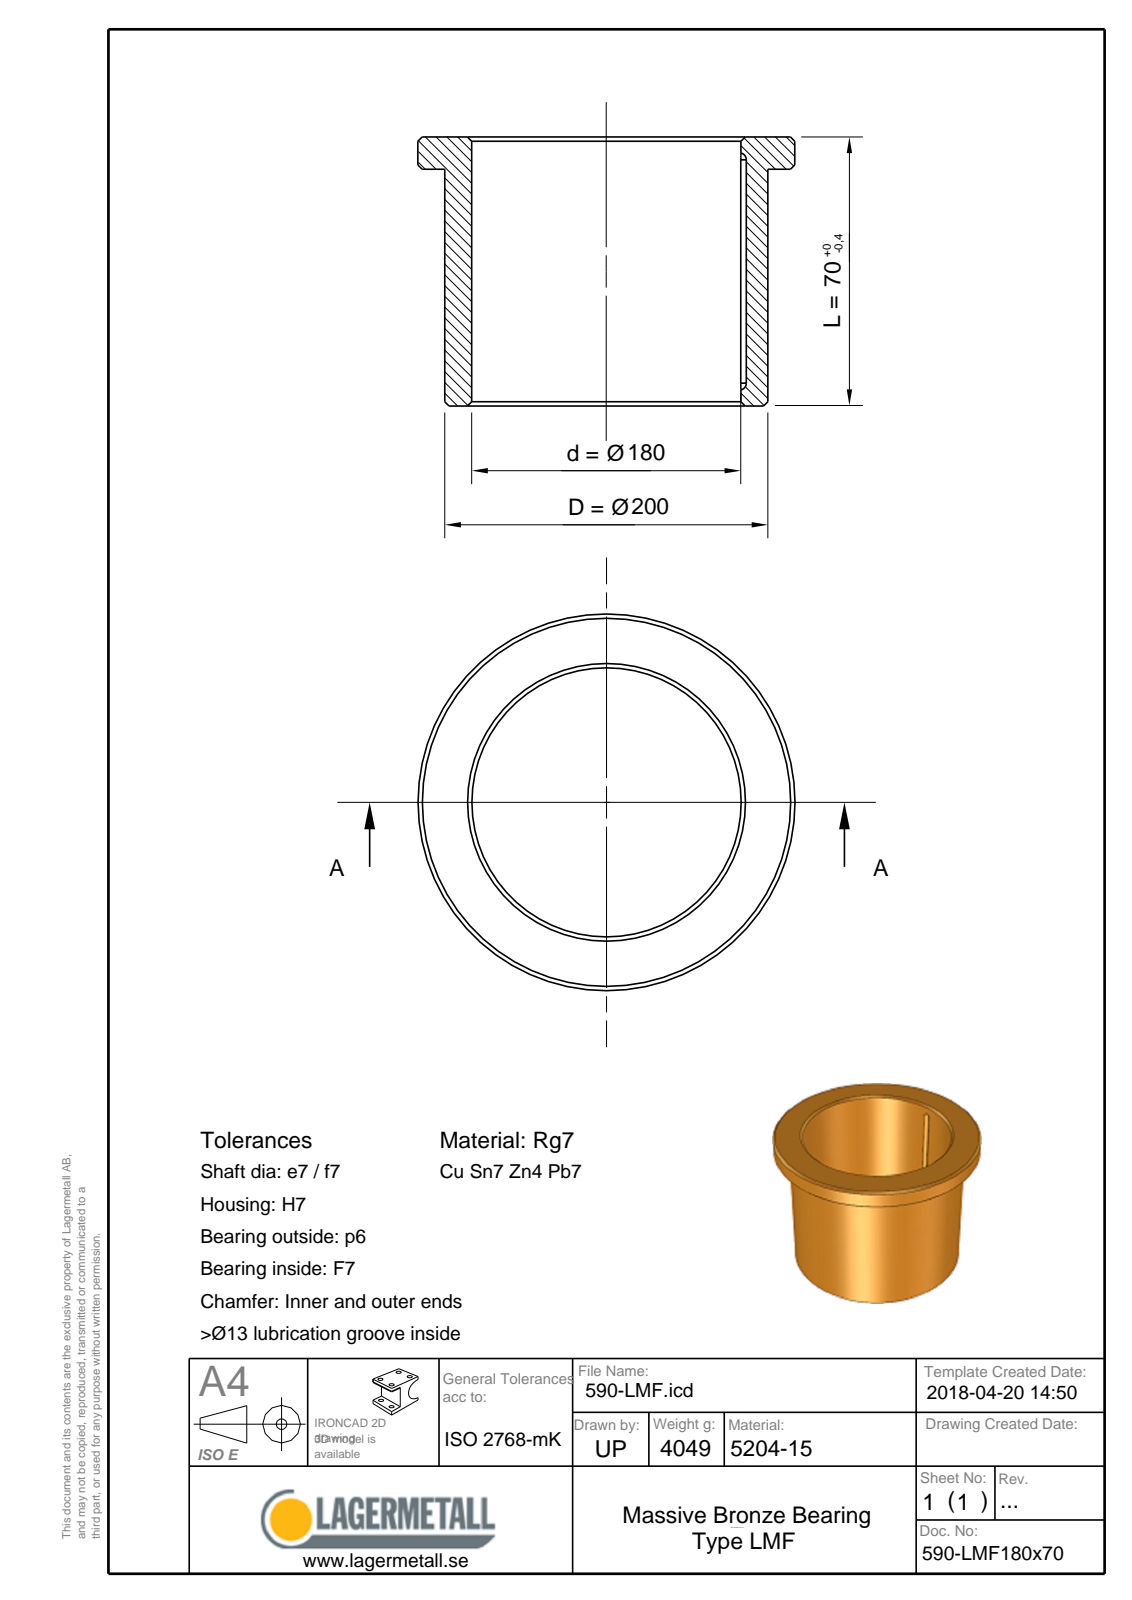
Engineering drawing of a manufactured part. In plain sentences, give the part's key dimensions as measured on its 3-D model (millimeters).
The part is named "590-LMF180x70". Its 3-D file was written by "Spatial InterOp 3D (CONFIG_CONTROL_DESIGN)". It is 1 solid with 16 faces: 4 planar, 5 cylindrical and 7 other. Overall it measures 215 by 215 by 70 millimeters. Its volume is 460 107 cubic millimeters and its surface area 102 237 square millimeters. Round holes: 1 of diameter 180. Round bosses or shafts: 1 of diameter 215, 1 of diameter 200. Partial cylindrical surfaces (rounded edges, fillets, slot ends): 2 of radius 2.25. The main face-to-face distances are 70, 60, 10.
